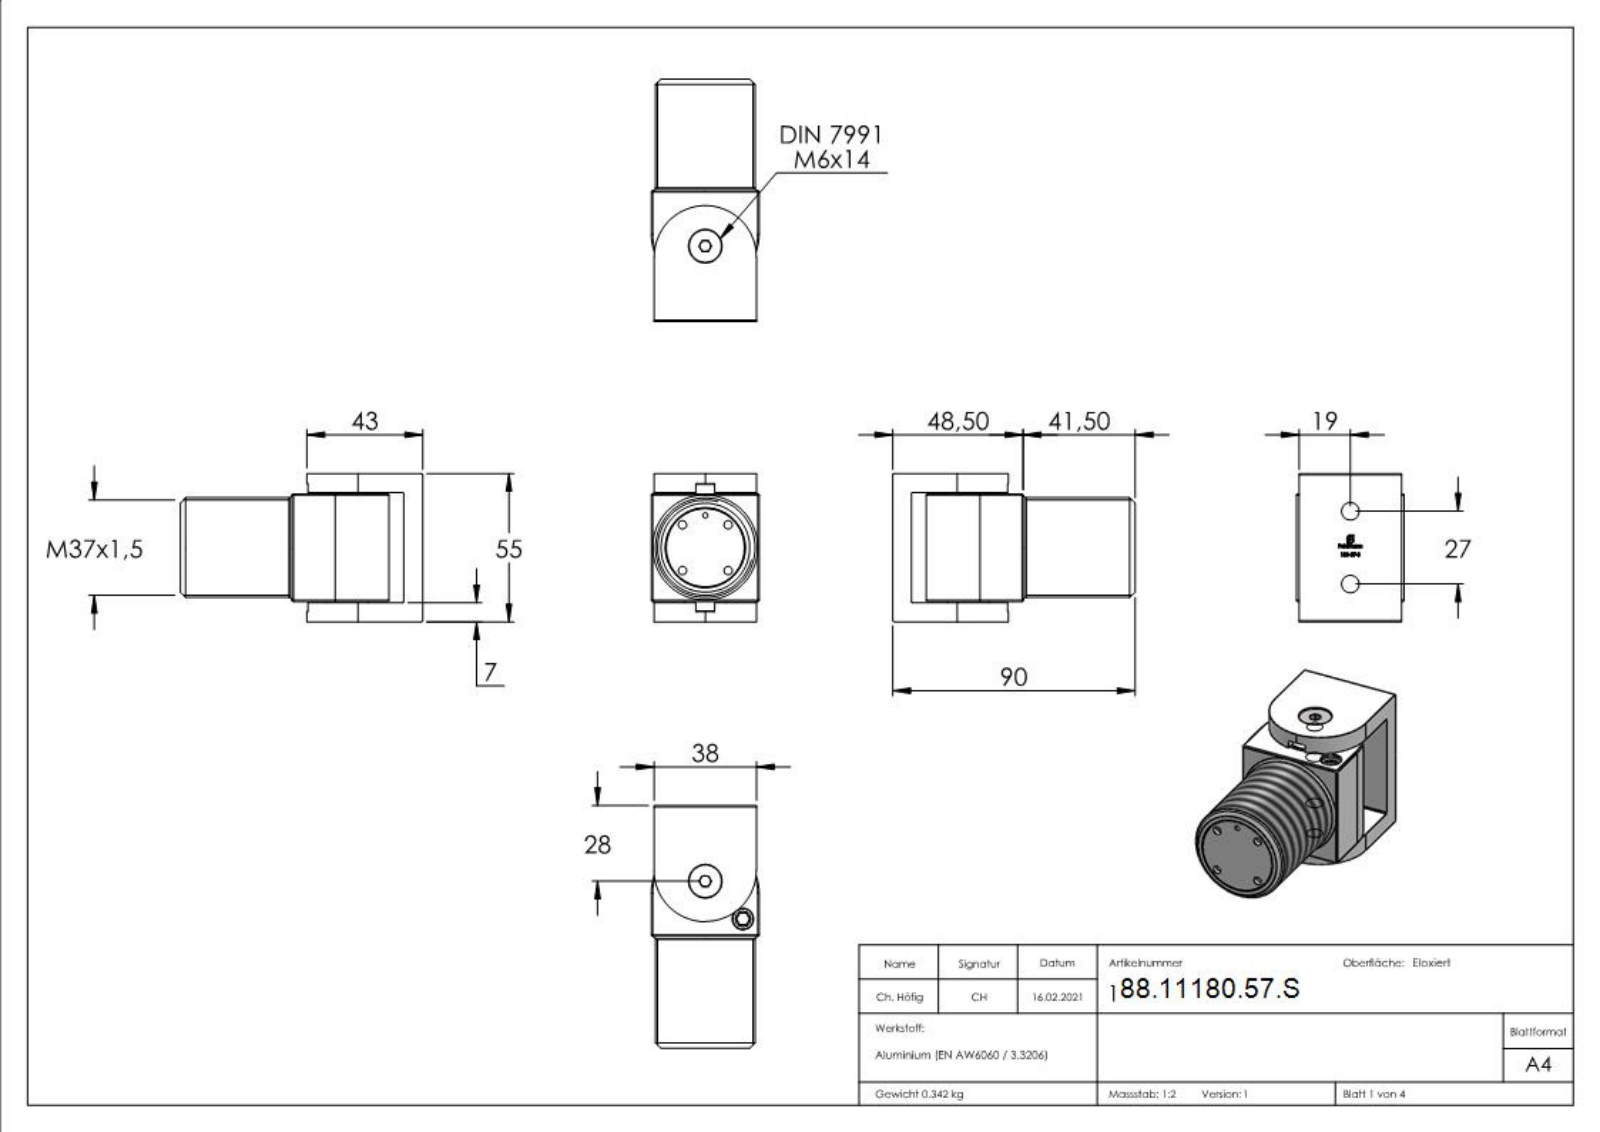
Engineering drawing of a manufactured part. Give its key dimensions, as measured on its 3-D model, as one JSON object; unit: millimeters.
{"part_name": "180-57-S; DIN-7991 M3-M10_DIN7991 M6x14; Teil1_180-57-S Teil1; Teil2_180-57-S Teil2", "step_written_by": "SolidWorks 2018 (CONFIG_CONTROL_DESIGN)", "units": "millimeters", "bodies": {"solids": 5, "faces": 471, "planar": 219, "cylindrical": 81, "other": 171}, "overall_size": [90, 55, 40], "volume_mm3": 124821, "surface_area_mm2": 27175, "round_holes": [[3.1, 4], [6.5, 3], [12.5, 3], [1.9, 1], [5, 1], [8, 1], [15.7, 1], [24, 1], [29.7, 1]], "round_bosses_or_shafts": [[37, 1], [29.5, 1], [26, 1], [23.6, 1], [15.5, 1], [12, 1], [7.8, 1], [6, 1]], "partial_cylinders_radius": [[0.5, 12], [19, 1], [20, 1]], "face_to_face_distances": [7, 48, 47.5, 0.5, 7.5, 40.5, 55, 40, 1, 39], "hole_center_spacings": [9.86, 12.01, 16.98, 23.57, 9.19, 13.5, 22.18, 24.01]}
